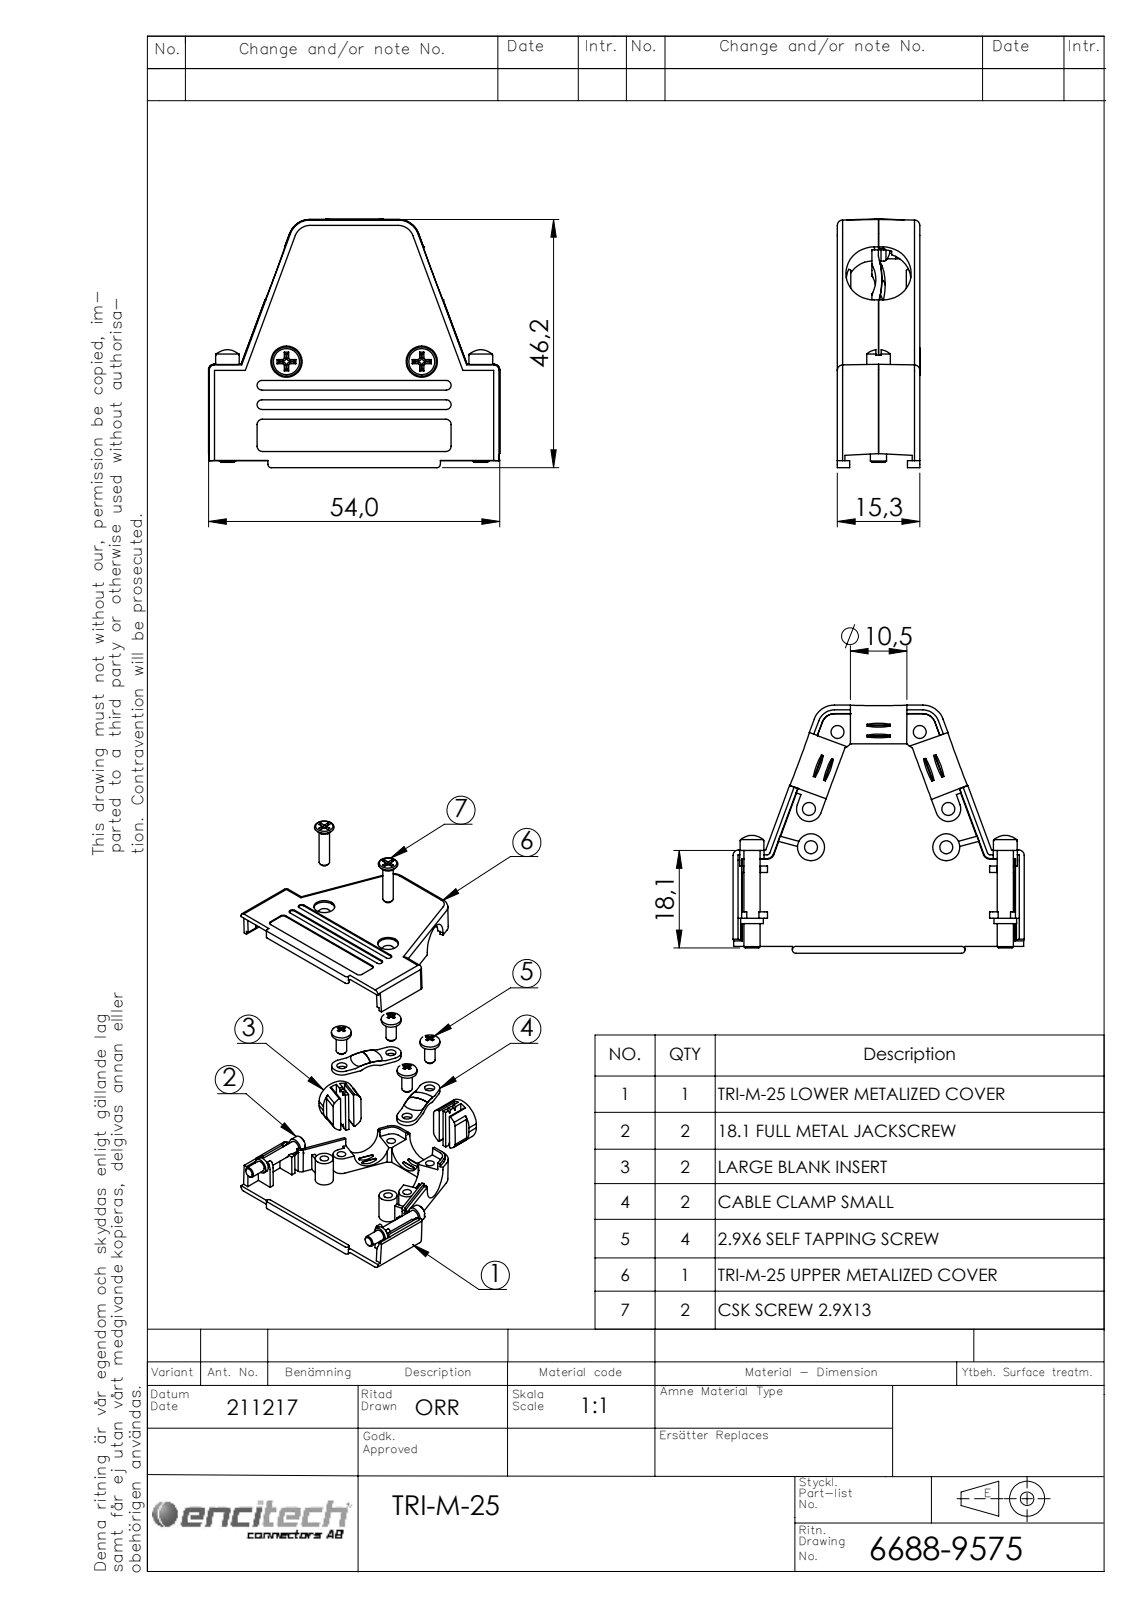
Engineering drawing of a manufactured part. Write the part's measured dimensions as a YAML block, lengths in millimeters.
part_name: "6805-0100-13; 6830-0106-01; 6550-0100-03; 6522-0128-33 (+4 more)"
step_written_by: "SolidWorks 2021 (AUTOMOTIVE_DESIGN)"
units: millimeters
bodies: {solids: 18, faces: 838, planar: 489, cylindrical: 226, other: 123}
overall_size: [54, 46.19, 15.33]
volume: 10355
surface_area: 15741
round_holes:
  - {diameter: 2.4, count: 6}
  - {diameter: 2.8, count: 4}
  - {diameter: 3.2, count: 4}
  - {diameter: 4.5, count: 2}
  - {diameter: 5.2, count: 2}
  - {diameter: 5.8, count: 2}
round_bosses_or_shafts:
  - {diameter: 2.9, count: 6}
  - {diameter: 5.5, count: 4}
  - {diameter: 7, count: 2}
  - {diameter: 5, count: 2}
  - {diameter: 4.4, count: 2}
  - {diameter: 4.2, count: 2}
  - {diameter: 3, count: 2}
partial_cylinders:
  - {radius: 1, count: 21}
  - {radius: 0.25, count: 10}
  - {radius: 0.5, count: 10}
  - {radius: 1.25, count: 10}
  - {radius: 1.5, count: 8}
  - {radius: 5.25, count: 5}
  - {radius: 0.9, count: 4}
  - {radius: 1.79, count: 4}
face_to_face_distances: [13.9, 1.4, 15.3, 12.5, 13.6, 15, 1.1, 6.25, 1.6, 1]
hole_center_spacings: [15.25, 7.11, 15.14, 15.26, 21.96, 26.4, 26.44, 29.41]
